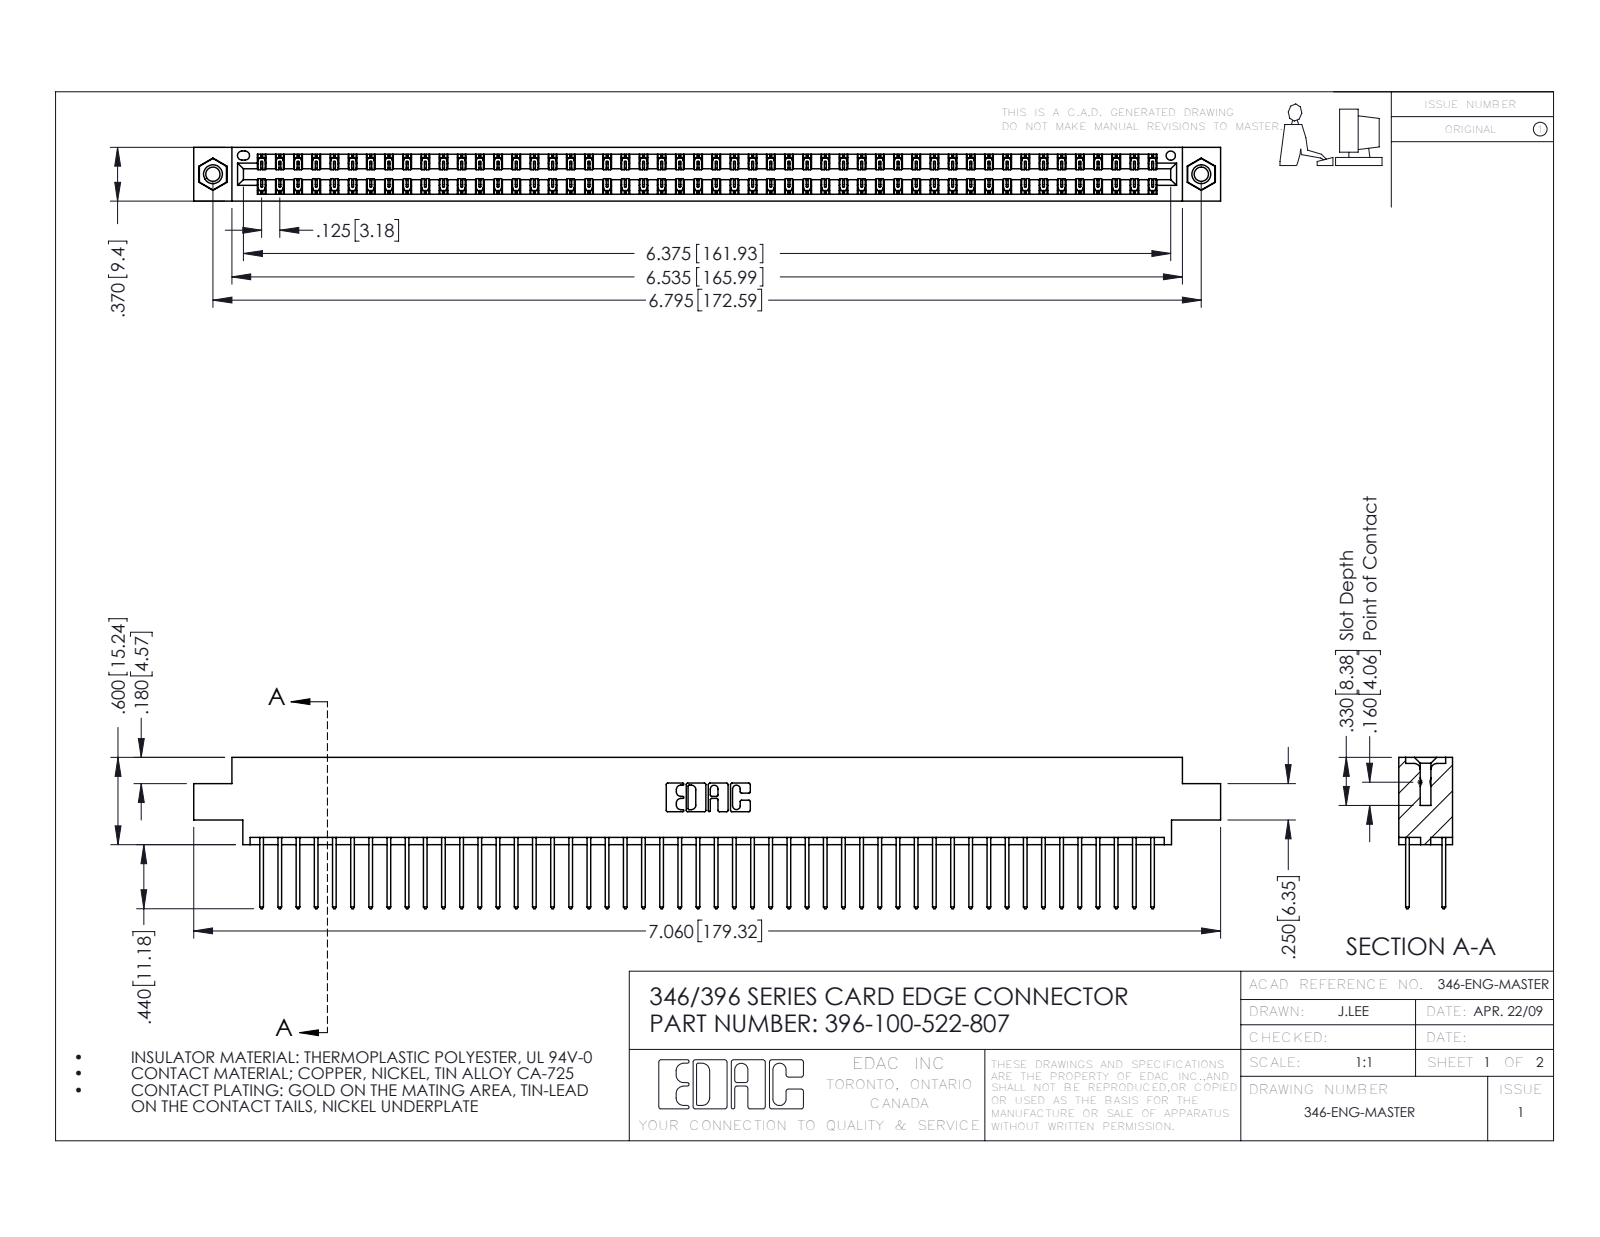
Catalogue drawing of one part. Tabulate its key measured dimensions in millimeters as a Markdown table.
| quantity | value |
| --- | --- |
| part name | 346 Part_0.170 Offset - 0.156 Dia-TI; 396-100-522-807; 345-292-001_345-293-122; 345-250-001_345-250-005-103 |
| STEP written by | SolidWorks 2016 (CONFIG_CONTROL_DESIGN) |
| units | millimeters |
| bodies | 103 solids, 5386 faces (3612 planar, 1758 cylindrical, 16 other) |
| overall size | 179.3 × 26.4 × 9.4 |
| volume | 17 630 mm³ |
| surface area | 25 770 mm² |
| round holes (diameter × count) | 2.5 × 2, 3.2 × 2, 4 × 2, 1.6 × 1 |
| round bosses / shafts (diameter × count) | 3.9 × 2 |
| partial cylindrical surfaces (radius × count) | 0.2 × 150, 0.3 × 100, 0.3 × 22, 0.2 × 6, 0.8 × 6, 0.7 × 3, 0.4 × 2, 0.6 × 2 |
| main face-to-face distances | 1.2, 8.2, 6.4, 9.4, 1.8, 7.6, 0.6, 7, 5.6, 3.8 |
| hole center spacings | 6.2, 167.3, 172.6 |
